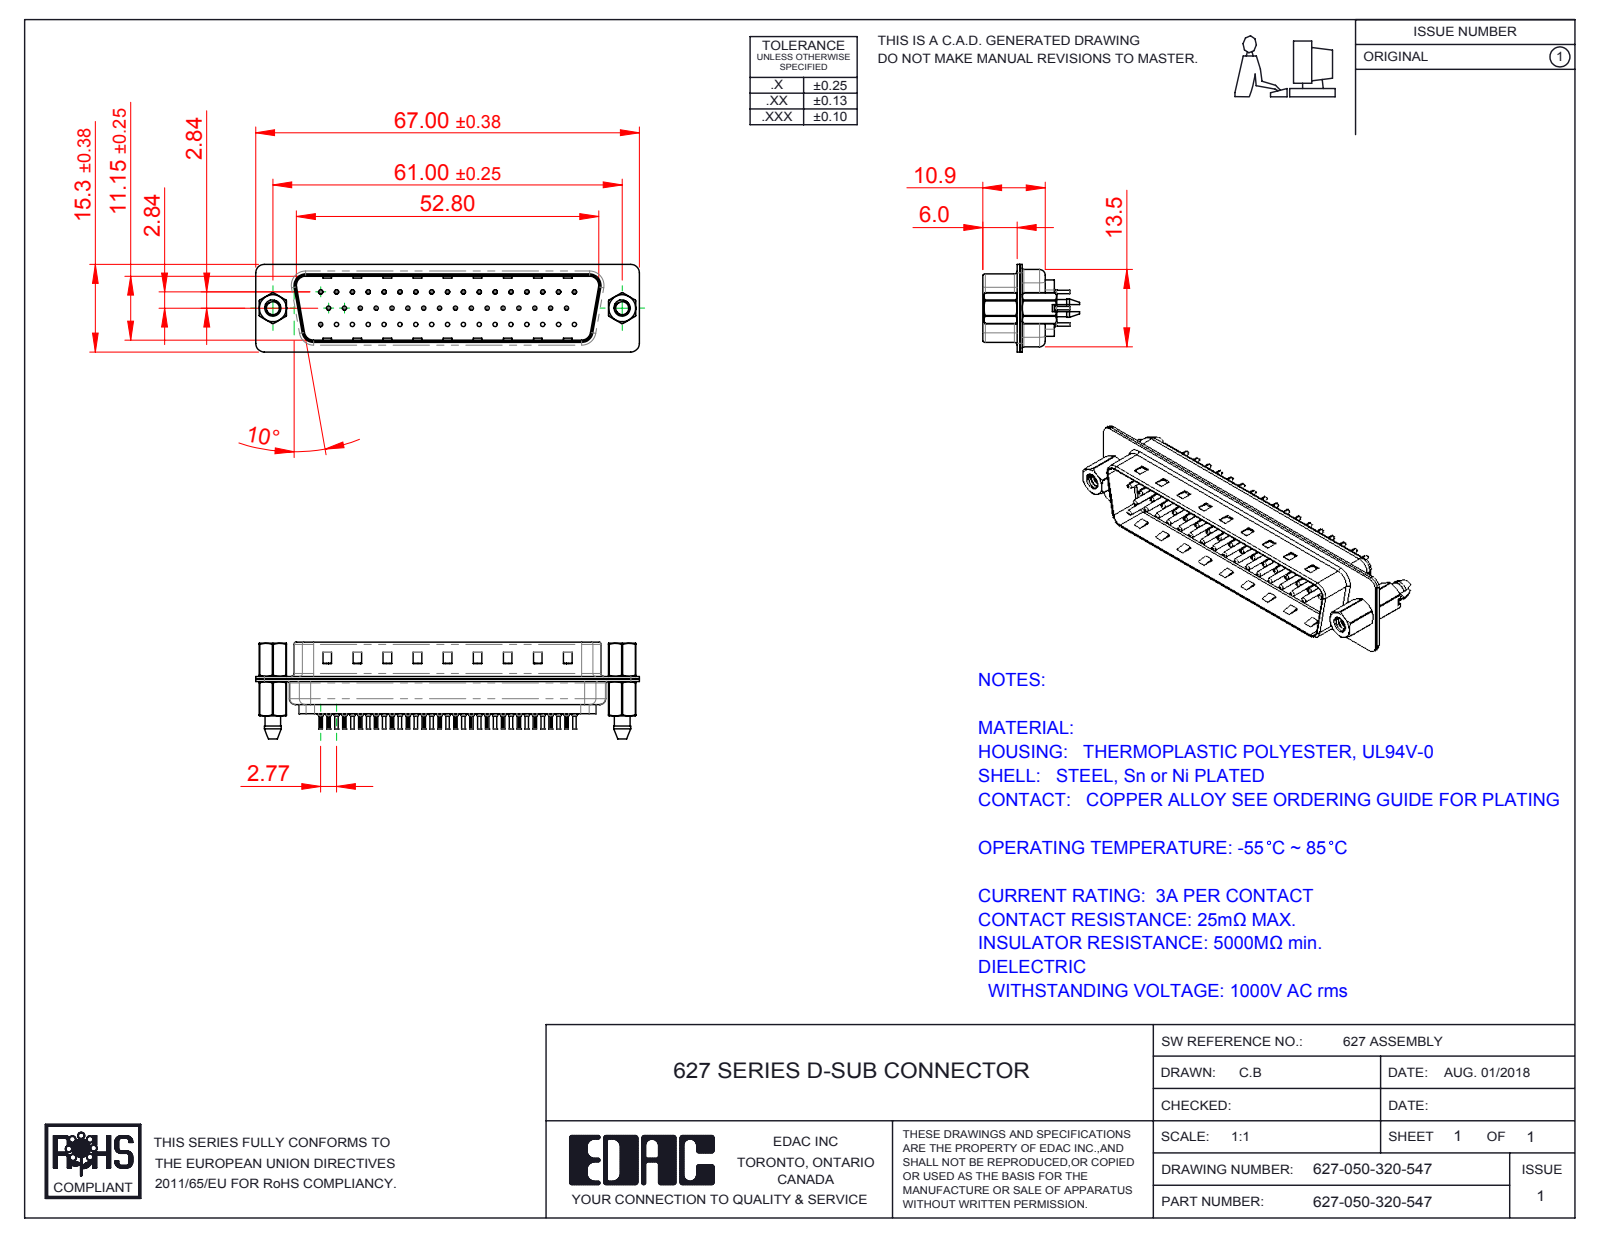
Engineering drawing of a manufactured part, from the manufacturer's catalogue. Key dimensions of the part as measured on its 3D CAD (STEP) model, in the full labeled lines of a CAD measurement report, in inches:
Part name (STEP PRODUCT): 627 Contact Row 2_20L; 627 Shell Rear_50 Contacts; 627 4-40 Threaded Boardlock_LP; 627 Contact Row 3_20L (+5 more)
STEP written by: SolidWorks 2016 (CONFIG_CONTROL_DESIGN)
Units: inches
Bodies: 41 solids, 4072 faces (1105 planar, 1599 cylindrical, 1368 other)
Overall size (bounding box): 2.638 × 0.665 × 0.602
Volume: 0.281 in³ · Surface area: 18.18 in²
Round holes (diameter × count): ⌀0.063 ×50, ⌀0.008 ×34, ⌀0.014 ×34, ⌀0.043 ×34, ⌀0.03 ×16, ⌀0.079 ×16, ⌀0.089 ×2, ⌀0.09 ×2, ⌀0.157 ×2, ⌀0.189 ×2
Round bosses / shafts (diameter × count): ⌀0.079 ×34, ⌀0.059 ×34, ⌀0.03 ×34, ⌀0.024 ×34, ⌀0.193 ×2, ⌀0.11 ×2
Partial cylindrical surfaces — rounded edges, fillets, slot ends (radius × count): R0.004 ×68, R0.059 ×18, R0.079 ×12, R0.063 ×10, R0.02 ×8, R0.01 ×4, R0.024 ×4, R0.026 ×4
Main face-to-face distances: 0.016, 0.018, 0.455, 0.035, 0.238, 0.256, 0.485, 0.031, 0.03, 0.485
Hole centre spacings: 0.124, 0.109, 0.218, 0.327, 0.436, 0.545, 0.654, 0.198
